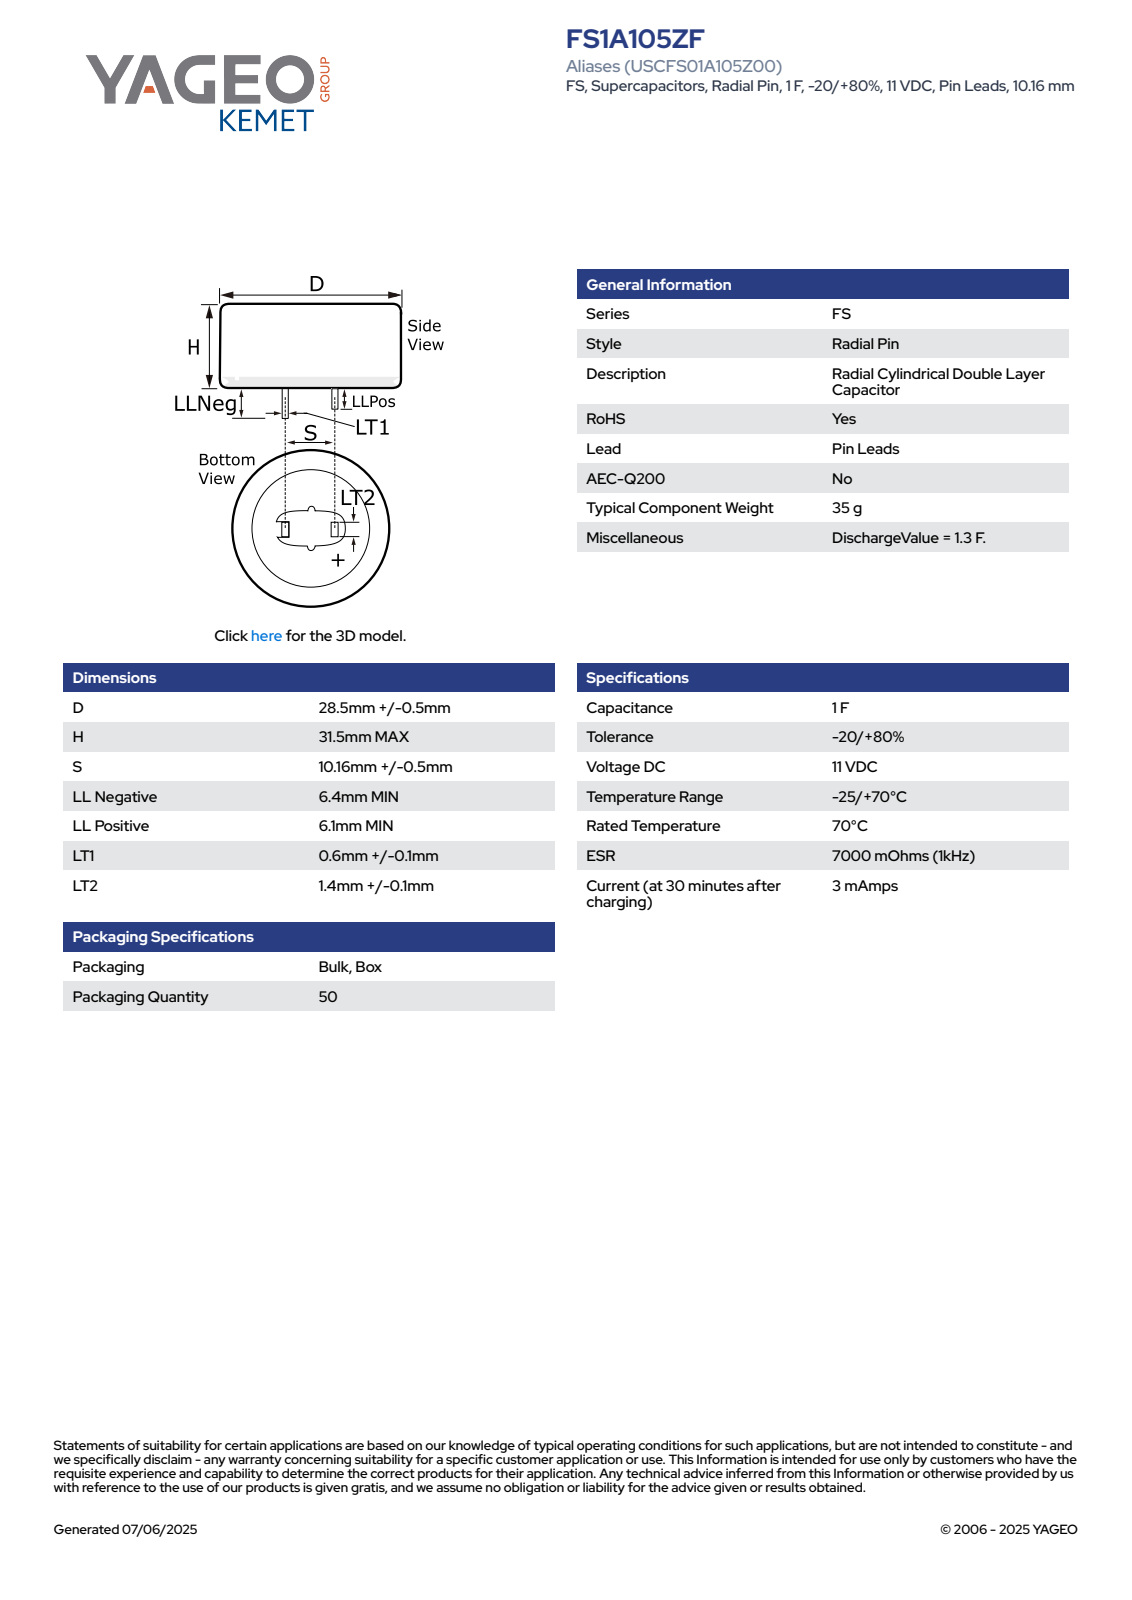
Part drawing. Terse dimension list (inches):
name: CDR_LPLLN_D29L31.5S10.16LLNEG6.4LLPOS6.1LT10.7LT21.5
written by: SolidWorks 2014 (AUTOMOTIVE_DESIGN)
unit: in
bodies: 1 solid, 78 faces (70 planar, 4 cylindrical, 4 other)
size: 1.492 × 1.142 × 1.142
volume: 1.261 in³; area: 6.33 in²
bosses: 1× ⌀1.142
rounds: 1× R0.571
face distances: 1.24, 0.028, 0.4, 0.372, 0.428, 0.059, 0.252, 1.492, 0.24, 1.48
